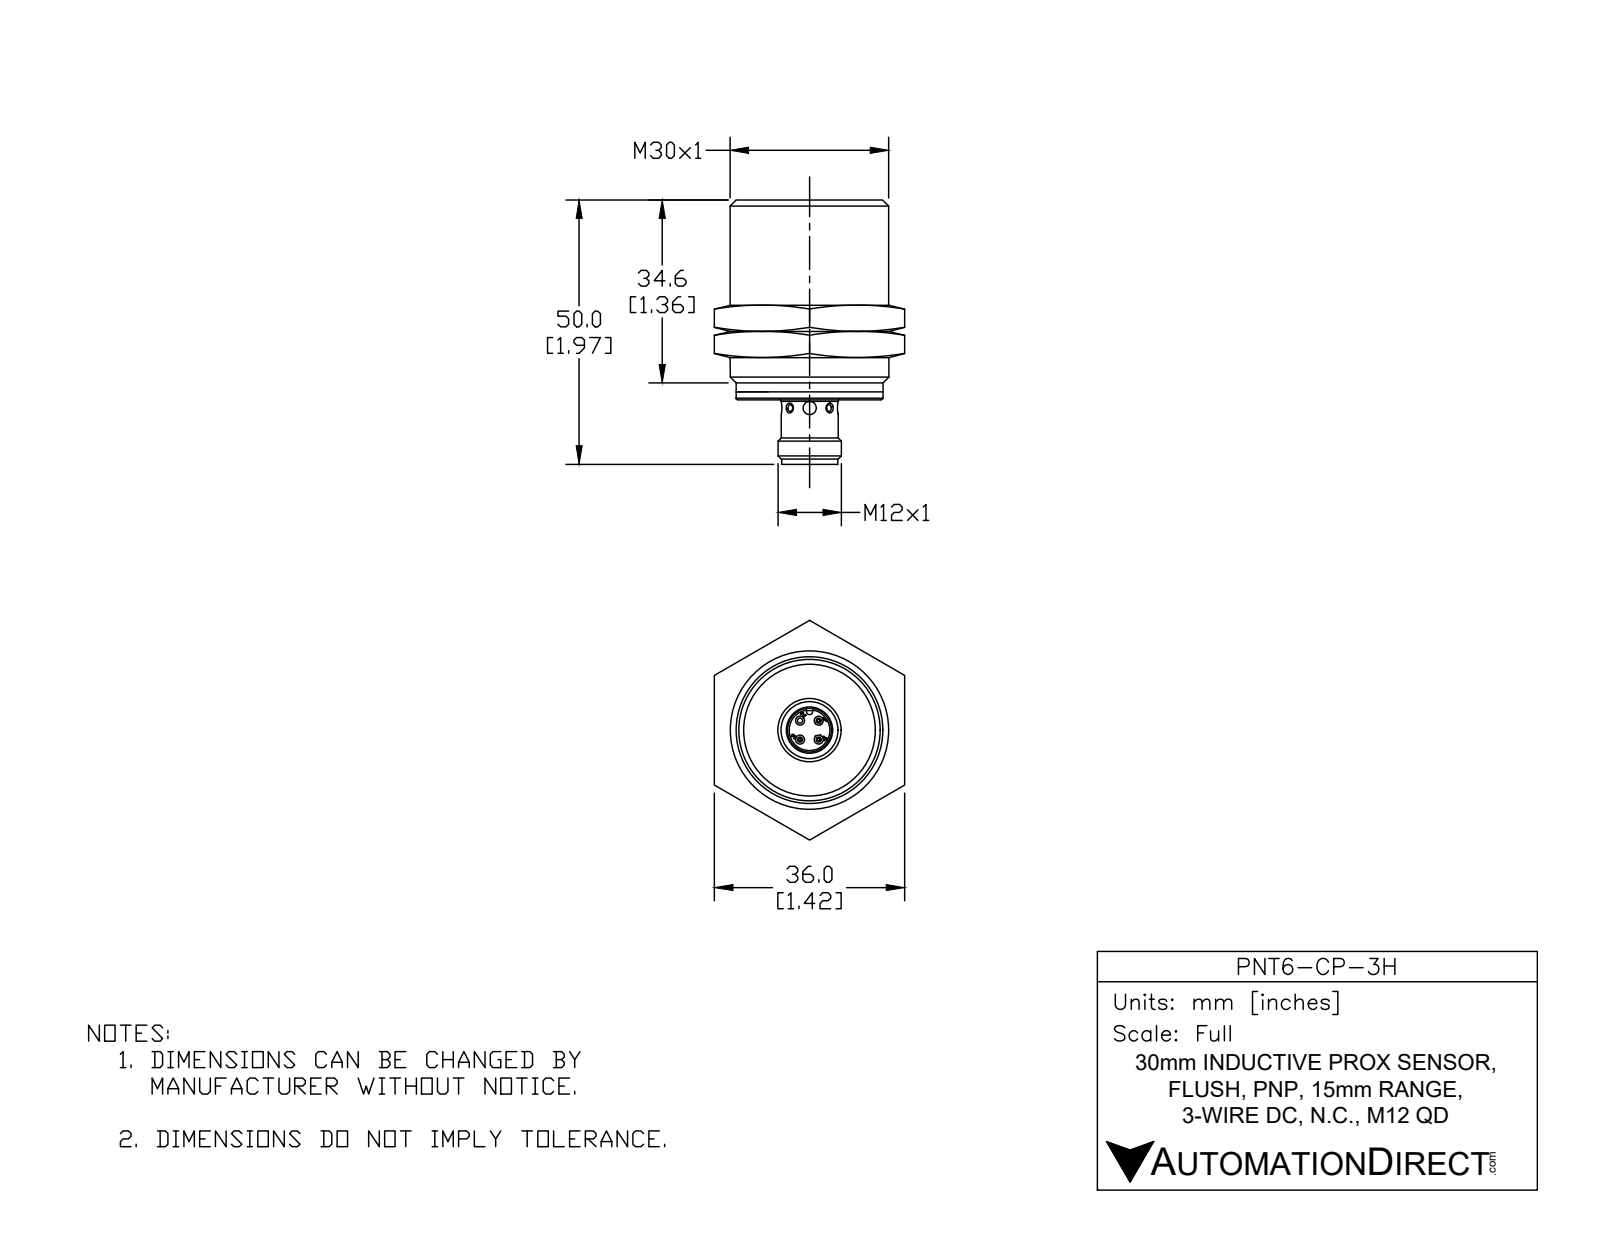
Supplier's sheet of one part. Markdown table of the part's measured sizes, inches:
| quantity | value |
| --- | --- |
| part name | PNT6-CP-3H |
| STEP written by | SolidWorks 2017 (AUTOMOTIVE_DESIGN) |
| units | inches |
| bodies | 1 solid, 515 faces (161 planar, 130 cylindrical, 224 other) |
| overall size | 1.969 × 1.181 × 1.181 |
| volume | 1.573 in³ |
| surface area | 12.79 in² |
| round holes (diameter × count) | 0.043 × 3, 0.04 × 2, 0.098 × 2, 0.038 × 1, 0.04 × 1, 0.323 × 1, 0.327 × 1, 0.394 × 1, 1.047 × 1, 1.076 × 1, 1.089 × 1 |
| round bosses / shafts (diameter × count) | 0.039 × 9, 1.181 × 1, 1.094 × 1, 1.083 × 1, 1.074 × 1, 1.044 × 1, 0.878 × 1, 0.472 × 1 |
| partial cylindrical surfaces (radius × count) | 0.004 × 12, 0.02 × 8, 0.03 × 3, 0.039 × 3, 0.024 × 1, 0.031 × 1 |
| main face-to-face distances | 0.126, 1.488, 1.362, 0.037, 0.089, 1.451, 0.098, 1.461, 0.028, 0.024 |
| hole center spacings | 0.098, 0.139, 0.197 |
